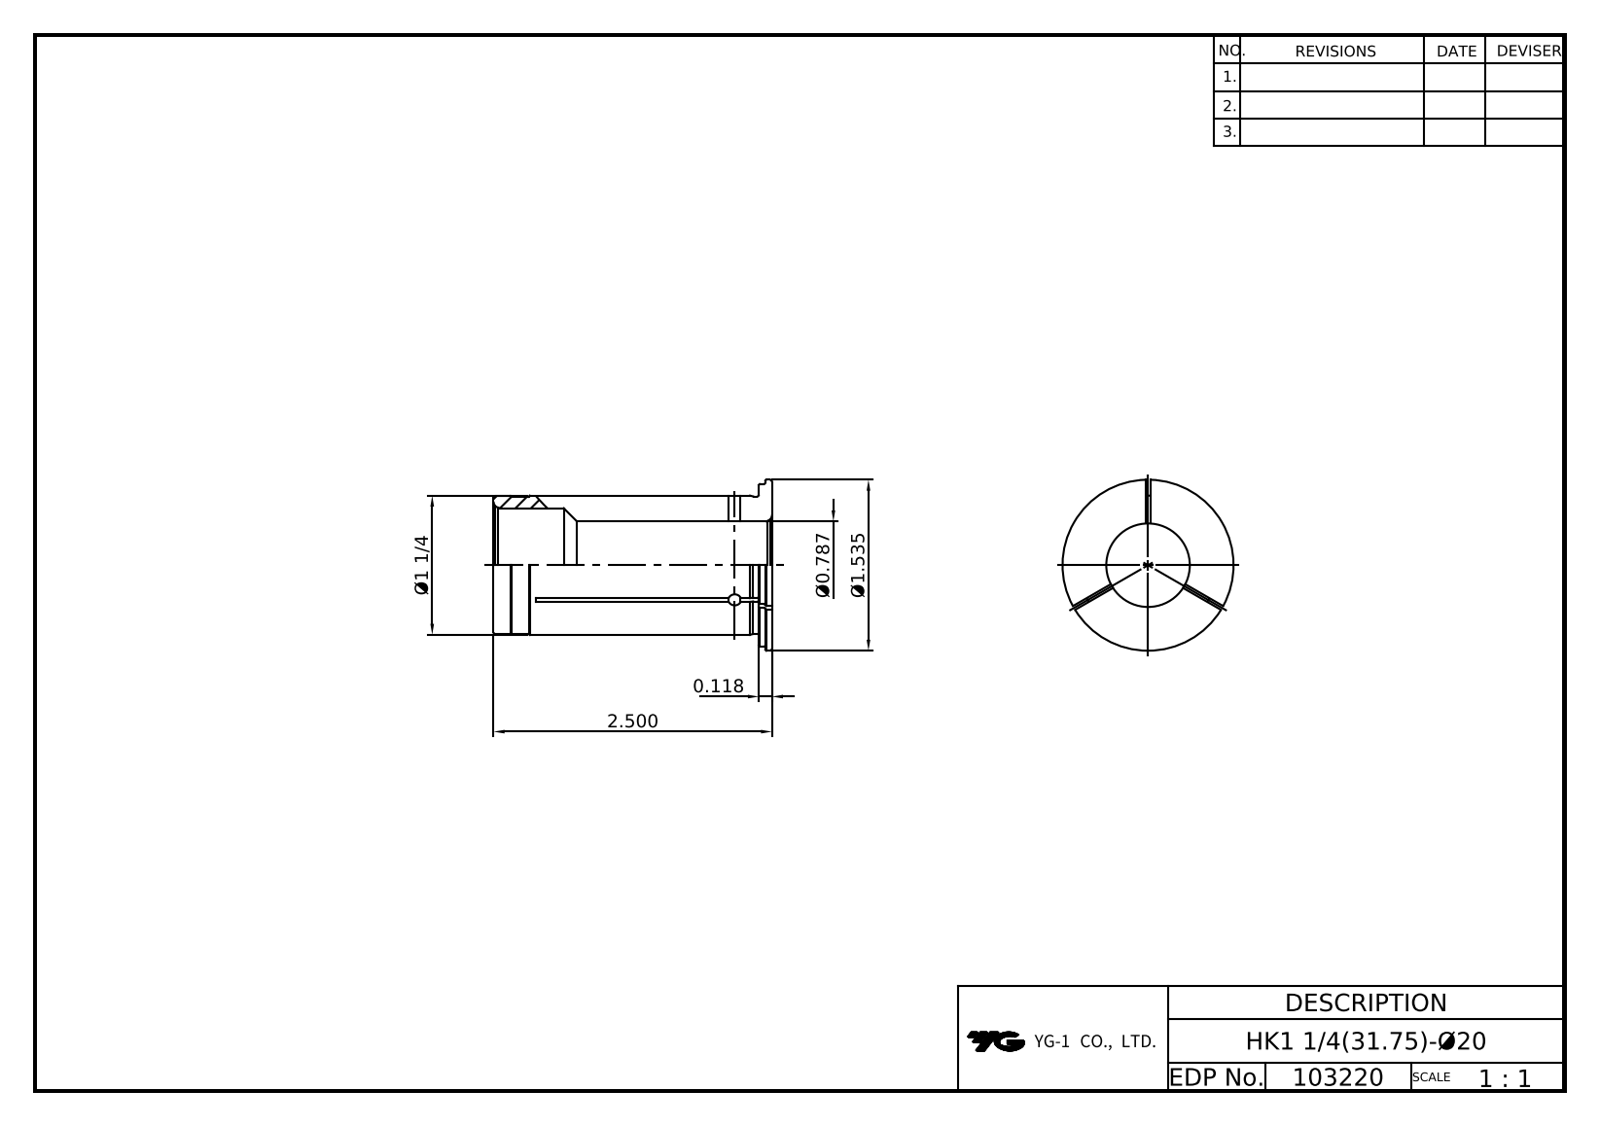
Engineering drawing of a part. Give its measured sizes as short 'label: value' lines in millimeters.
name: LO-HK31.75-20
written by: Autodesk Inventor 2025 (AP242_MANAGED_MODEL_BASED_3D_ENGINEERING_MIM_LF)
unit: mm
bodies: 1 solid, 14 faces (4 planar, 5 cylindrical, 5 other)
size: 63.5 × 39 × 39
volume: 27 571 mm³; area: 12 277 mm²
holes: 1× ⌀20, 1× ⌀26
bosses: 1× ⌀39, 1× ⌀37, 1× ⌀31.75
face distances: 63.5, 60.5, 3, 1.5, 62
